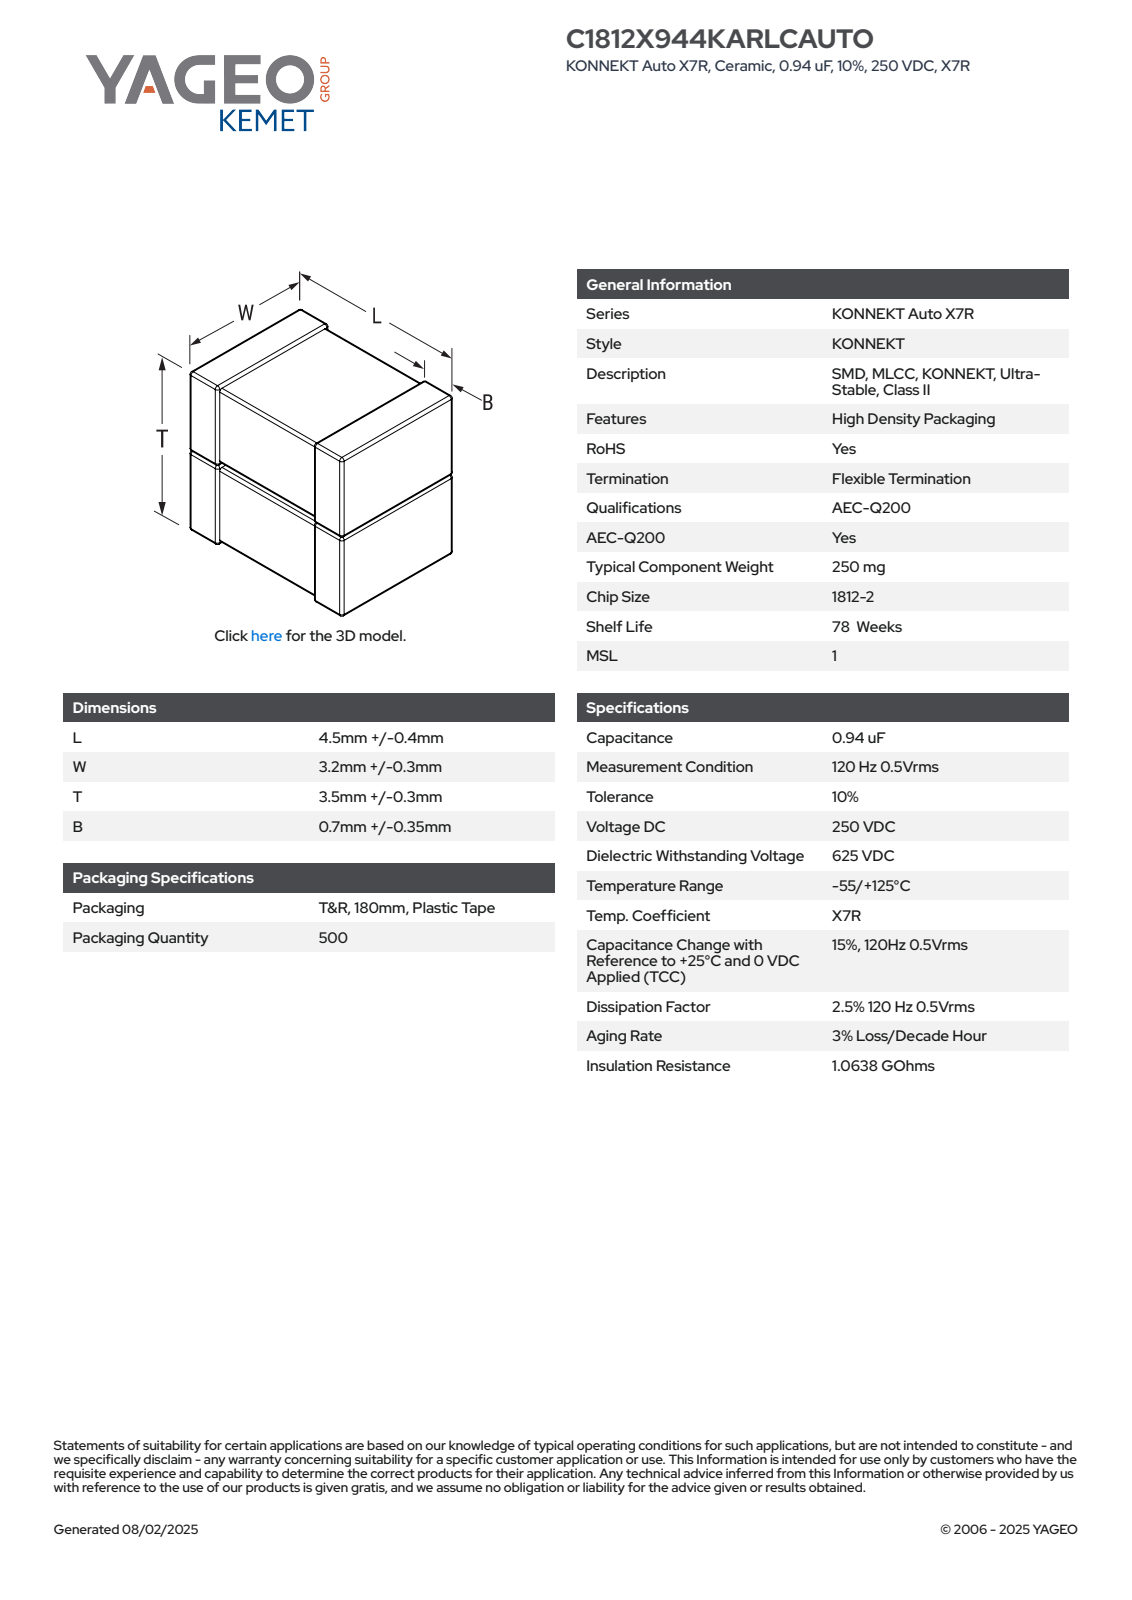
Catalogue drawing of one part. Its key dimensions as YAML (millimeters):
part_name: "CCSS_K2T_1812-2_L4.9W3.5B1.05T3.8"
step_written_by: "SolidWorks 2020 (AUTOMOTIVE_DESIGN)"
units: millimeters
bodies: {solids: 4, faces: 189, planar: 81, cylindrical: 76, other: 32}
overall_size: [4.9, 3.8, 3.5]
volume: 61
surface_area: 117
face_to_face_distances: [1.76, 1.9, 3.43, 1.83, 1.97, 3.73, 4.9, 3.36, 3.66, 3.5]
